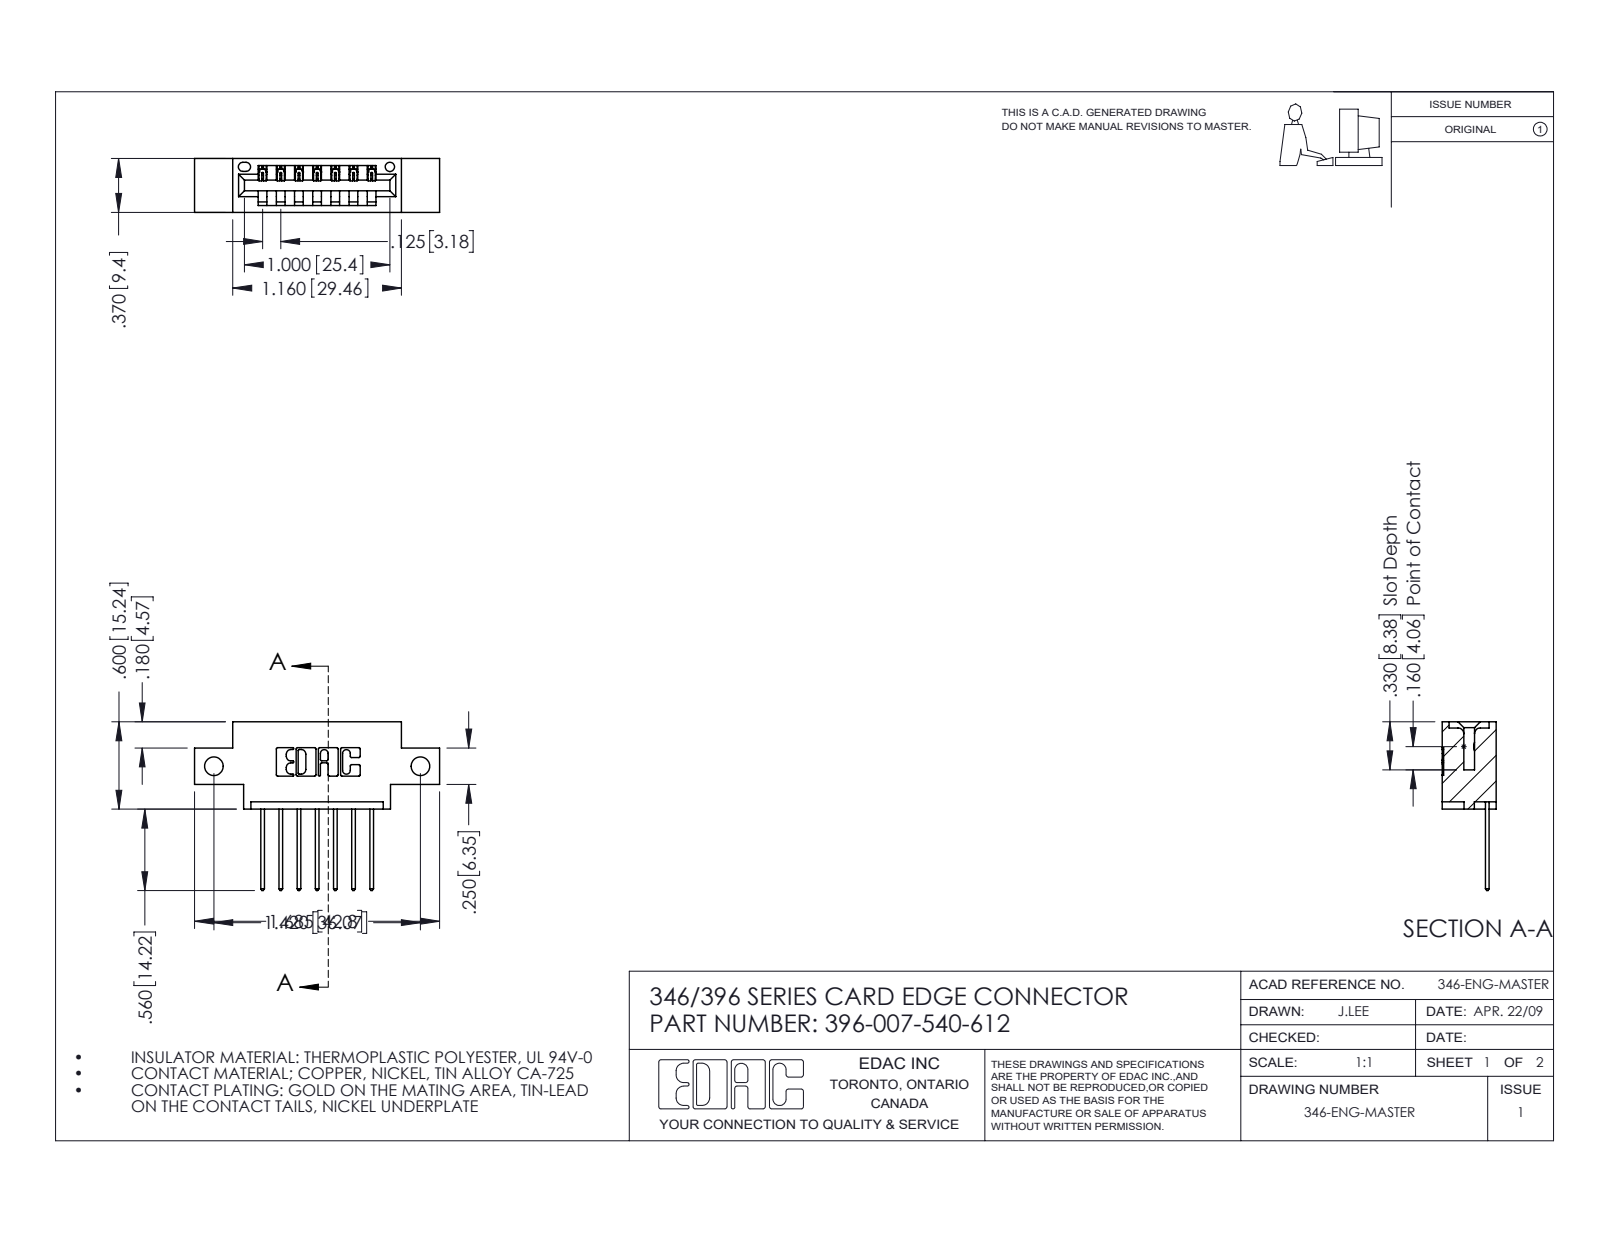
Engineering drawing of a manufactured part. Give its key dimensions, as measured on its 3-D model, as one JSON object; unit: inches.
{"part_name": "346 Part_0.170 Offset - Side Mount; 345-292-001_345-293-140; 396-007-540-612", "step_written_by": "SolidWorks 2016 (CONFIG_CONTROL_DESIGN)", "units": "inches", "bodies": {"solids": 8, "faces": 532, "planar": 360, "cylindrical": 172, "other": 0}, "overall_size": [1.685, 1.16, 0.37], "volume_in3": 0.221, "surface_area_in2": 6.564, "round_holes": [[0.128, 2], [0.064, 1]], "partial_cylinders_radius": [[0.01, 22], [0.006, 14], [0.01, 14], [0.007, 6], [0.031, 6], [0.026, 3], [0.031, 2], [0.04, 2]], "face_to_face_distances": [0.25, 0.37, 0.048, 0.322, 0.072, 0.298, 0.025, 0.148, 0.222, 0.1], "hole_center_spacings": [1.42]}
